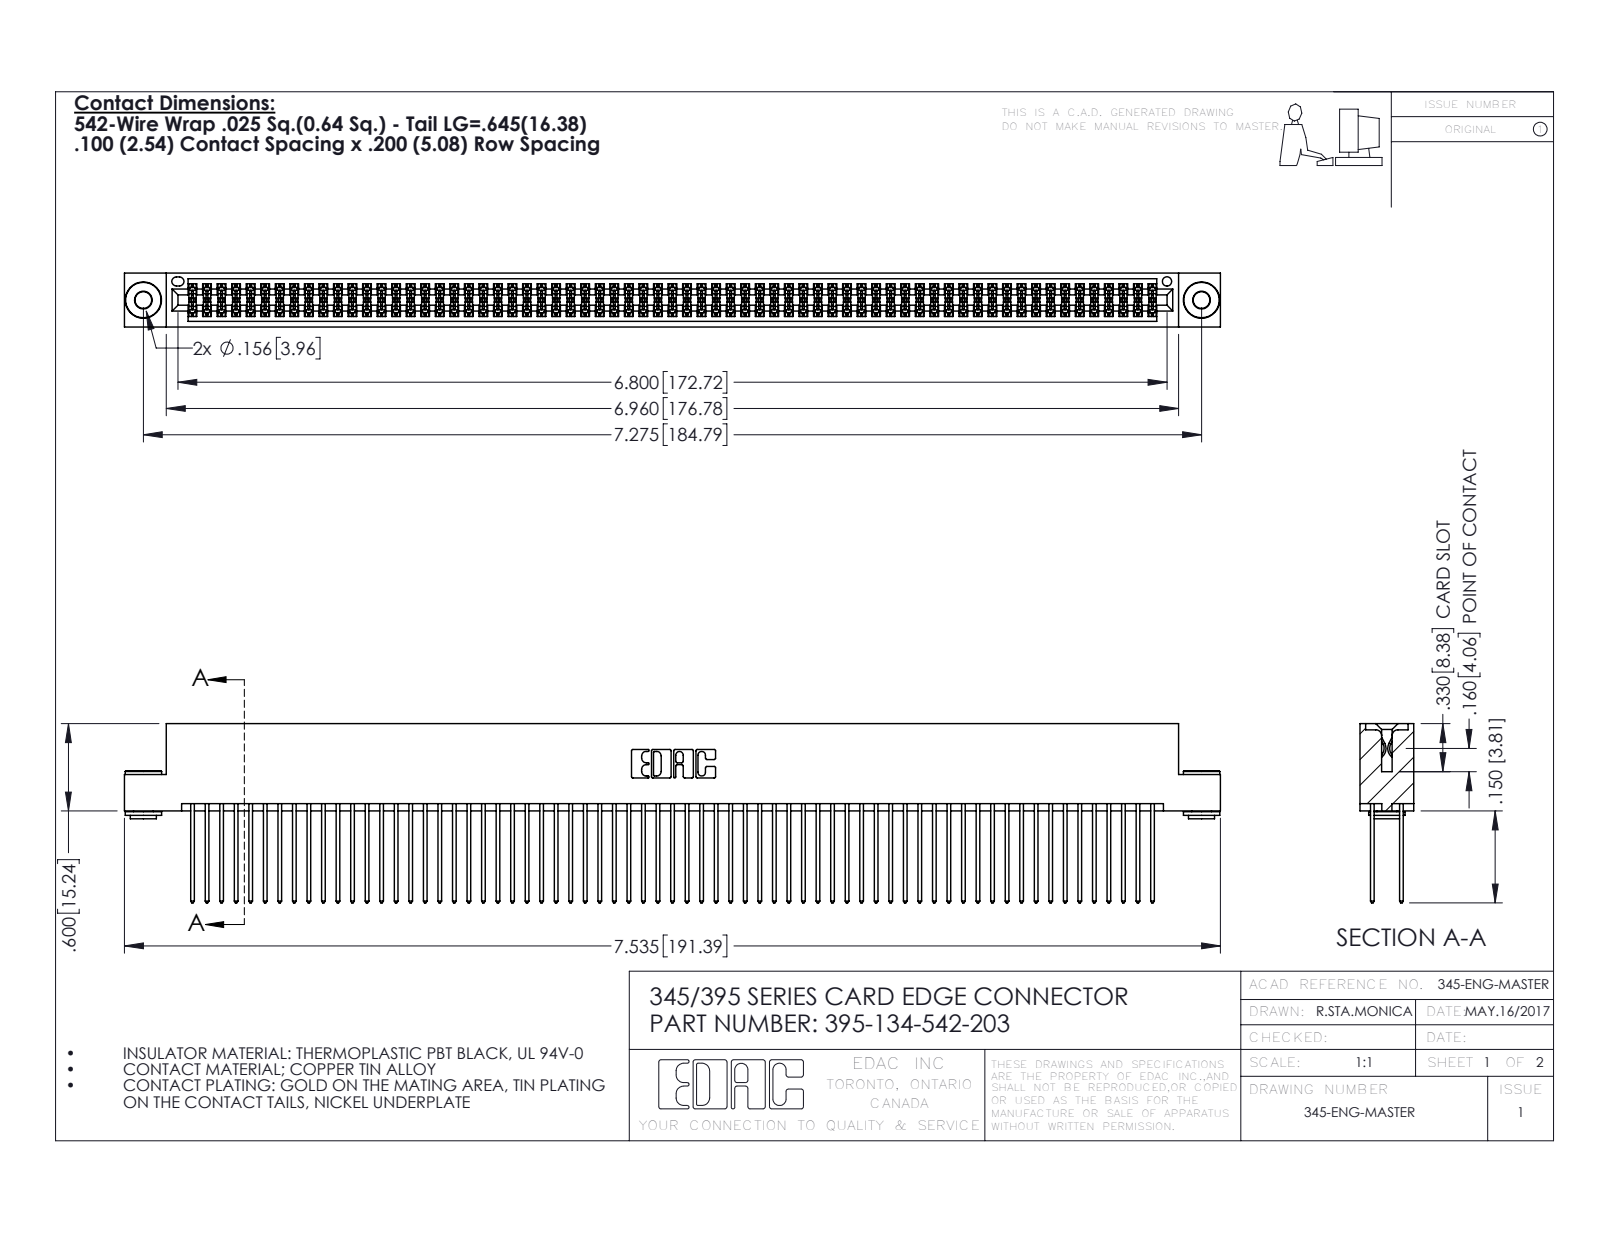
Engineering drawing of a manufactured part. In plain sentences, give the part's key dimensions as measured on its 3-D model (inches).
The part is named "395-134-542-203; 345-292-001_345-293-142; 345-250-002_345-250-002-102; 345 Part_Flush Mounting Lugs - 0.156 Dia-TH". Its 3-D file was written by "SolidWorks 2016 (CONFIG_CONTROL_DESIGN)". It is 137 solids with 6864 faces: 4512 planar, 2344 cylindrical and 8 other. Overall it measures 7.535 by 1.232 by 0.37 inches. Its volume is 1.188 cubic inches and its surface area 50.2 square inches. Round holes: 2 of diameter 0.116, 2 of diameter 0.156, 1 of diameter 0.064. Round bosses or shafts: 2 of diameter 0.25, 2 of diameter 0.18, 2 of diameter 0.136. Partial cylindrical surfaces (rounded edges, fillets, slot ends): 201 of radius 0.006, 134 of radius 0.01, 22 of radius 0.01, 6 of radius 0.007, 6 of radius 0.031, 3 of radius 0.026, 2 of radius 0.014, 2 of radius 0.019. The main face-to-face distances are 0.072, 0.298, 0.2, 0.025, 0.098, 0.272, 0.225, 0.37, 0.175, 0.149. The hole center spacings are 0.27, 7.039, 7.275.
